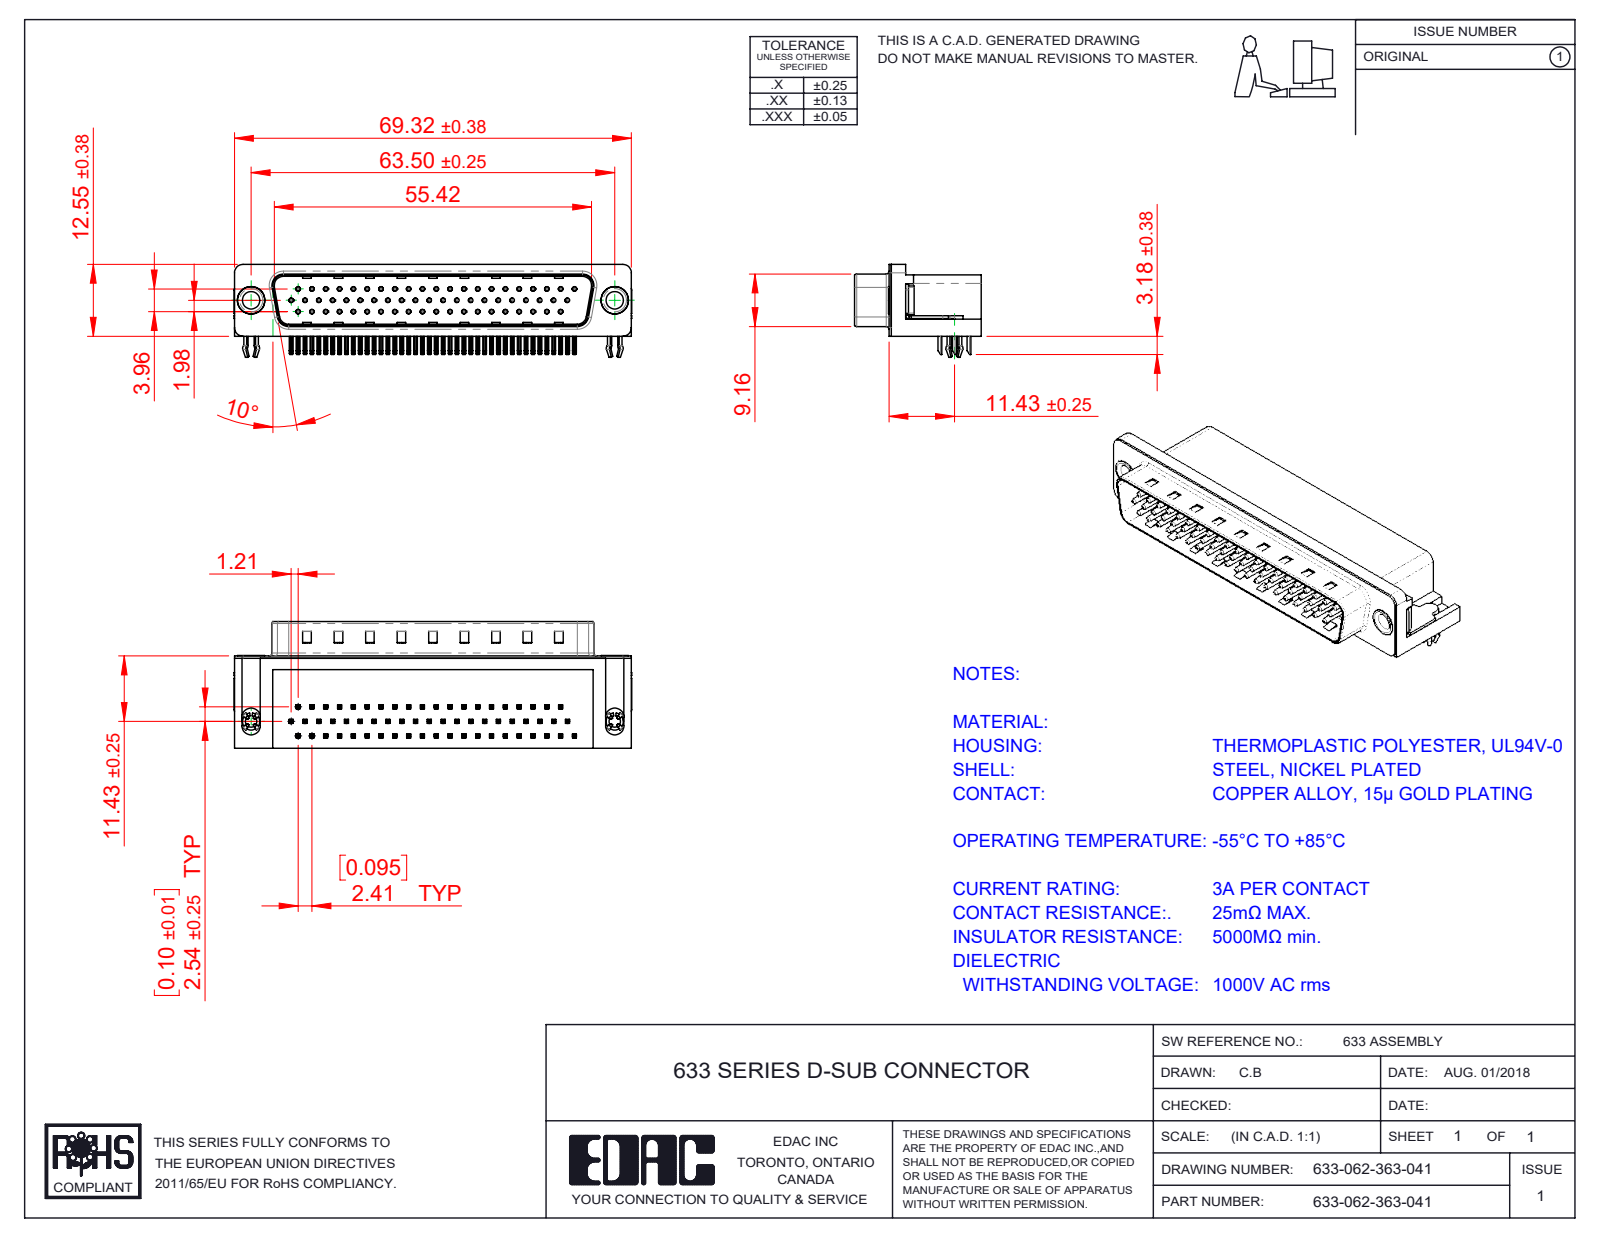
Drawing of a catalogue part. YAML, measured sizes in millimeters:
part_name: "633-062-363-041; 633 Housing_62 Contact; 633 Contact Top; 633 Contact Middle (+4 more)"
step_written_by: "SolidWorks 2016 (CONFIG_CONTROL_DESIGN)"
units: millimeters
bodies: {solids: 68, faces: 5156, planar: 3255, cylindrical: 1430, other: 471}
overall_size: [69.4, 22.1, 16.25]
volume: 11053
surface_area: 13460
round_holes:
  - {diameter: 0.35, count: 62}
  - {diameter: 0.8, count: 62}
  - {diameter: 2, count: 2}
  - {diameter: 3.05, count: 2}
  - {diameter: 4, count: 2}
  - {diameter: 4.8, count: 2}
  - {diameter: 5, count: 2}
round_bosses_or_shafts:
  - {diameter: 0.75, count: 62}
  - {diameter: 4.9, count: 2}
  - {diameter: 4.75, count: 2}
  - {diameter: 3.85, count: 2}
  - {diameter: 3, count: 2}
partial_cylinders:
  - {radius: 0.25, count: 260}
  - {radius: 0.12, count: 124}
  - {radius: 1, count: 16}
  - {radius: 0.5, count: 9}
  - {radius: 1.6, count: 8}
  - {radius: 1.5, count: 7}
  - {radius: 0.9, count: 4}
  - {radius: 2, count: 4}
face_to_face_distances: [0.4, 10.35, 15.7, 8.76, 2.9, 2.5, 2.54, 8.36, 2.1, 10.46]
hole_center_spacings: [2.41, 4.82, 7.24, 9.65, 14.48, 16.89, 4.83, 7.23]
